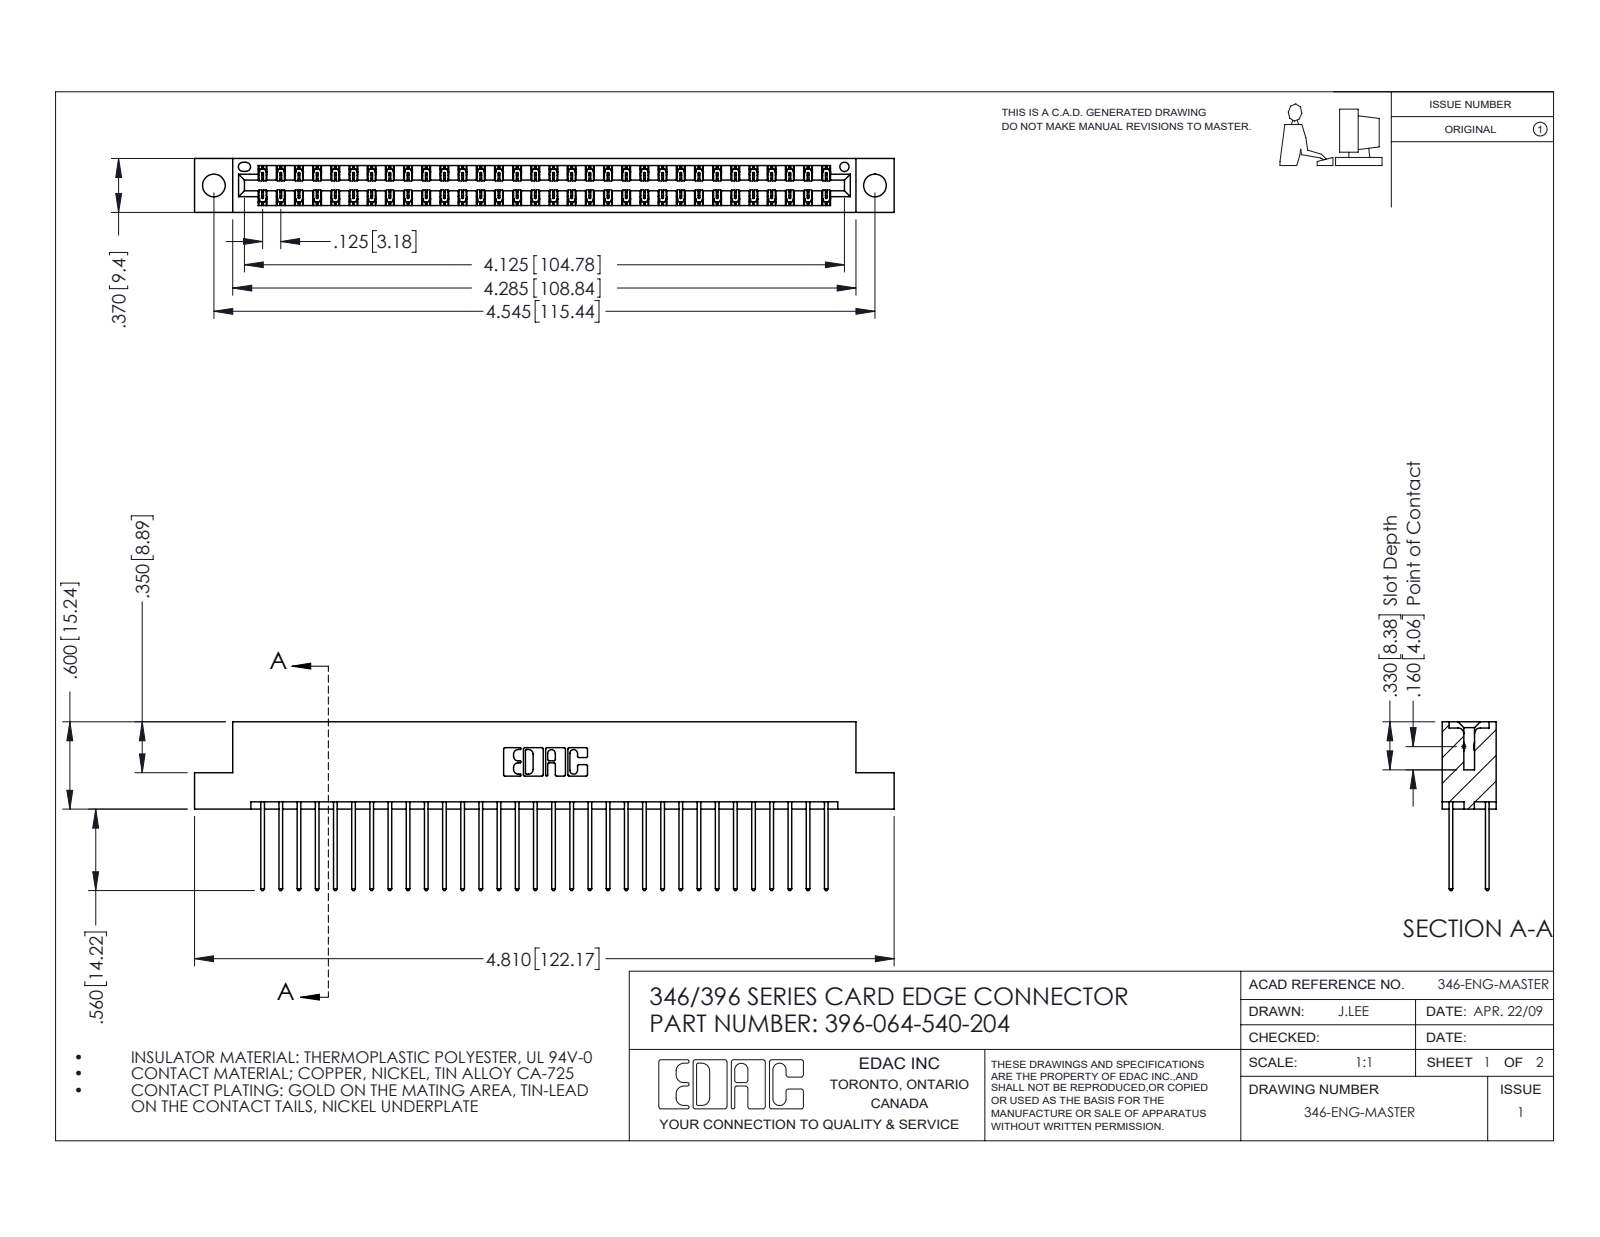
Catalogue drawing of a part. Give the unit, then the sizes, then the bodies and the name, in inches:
Units: inches
Overall size (bounding box): 4.81 × 1.16 × 0.37
Round holes (diameter × count): ⌀0.156 ×2, ⌀0.064 ×1
Partial cylindrical surfaces — rounded edges, fillets, slot ends (radius × count): R0.006 ×96, R0.01 ×64, R0.01 ×22, R0.007 ×6, R0.031 ×6, R0.026 ×3, R0.014 ×2, R0.022 ×2
Main face-to-face distances: 0.048, 0.322, 0.25, 0.072, 0.298, 0.025, 0.37, 0.275, 0.148, 0.222
Hole centre spacings: 0.246, 4.337, 4.545
Volume: 0.732 in³ · Surface area: 26.79 in²
Bodies: 65 solids, 3450 faces (2316 planar, 1134 cylindrical, 0 other)
Part name (STEP PRODUCT): 346 Part_Flush Mounting Lugs - 0.156 Dia-TH; 396-064-540-204; 345-292-001_345-293-140
STEP written by: SolidWorks 2016 (CONFIG_CONTROL_DESIGN)
